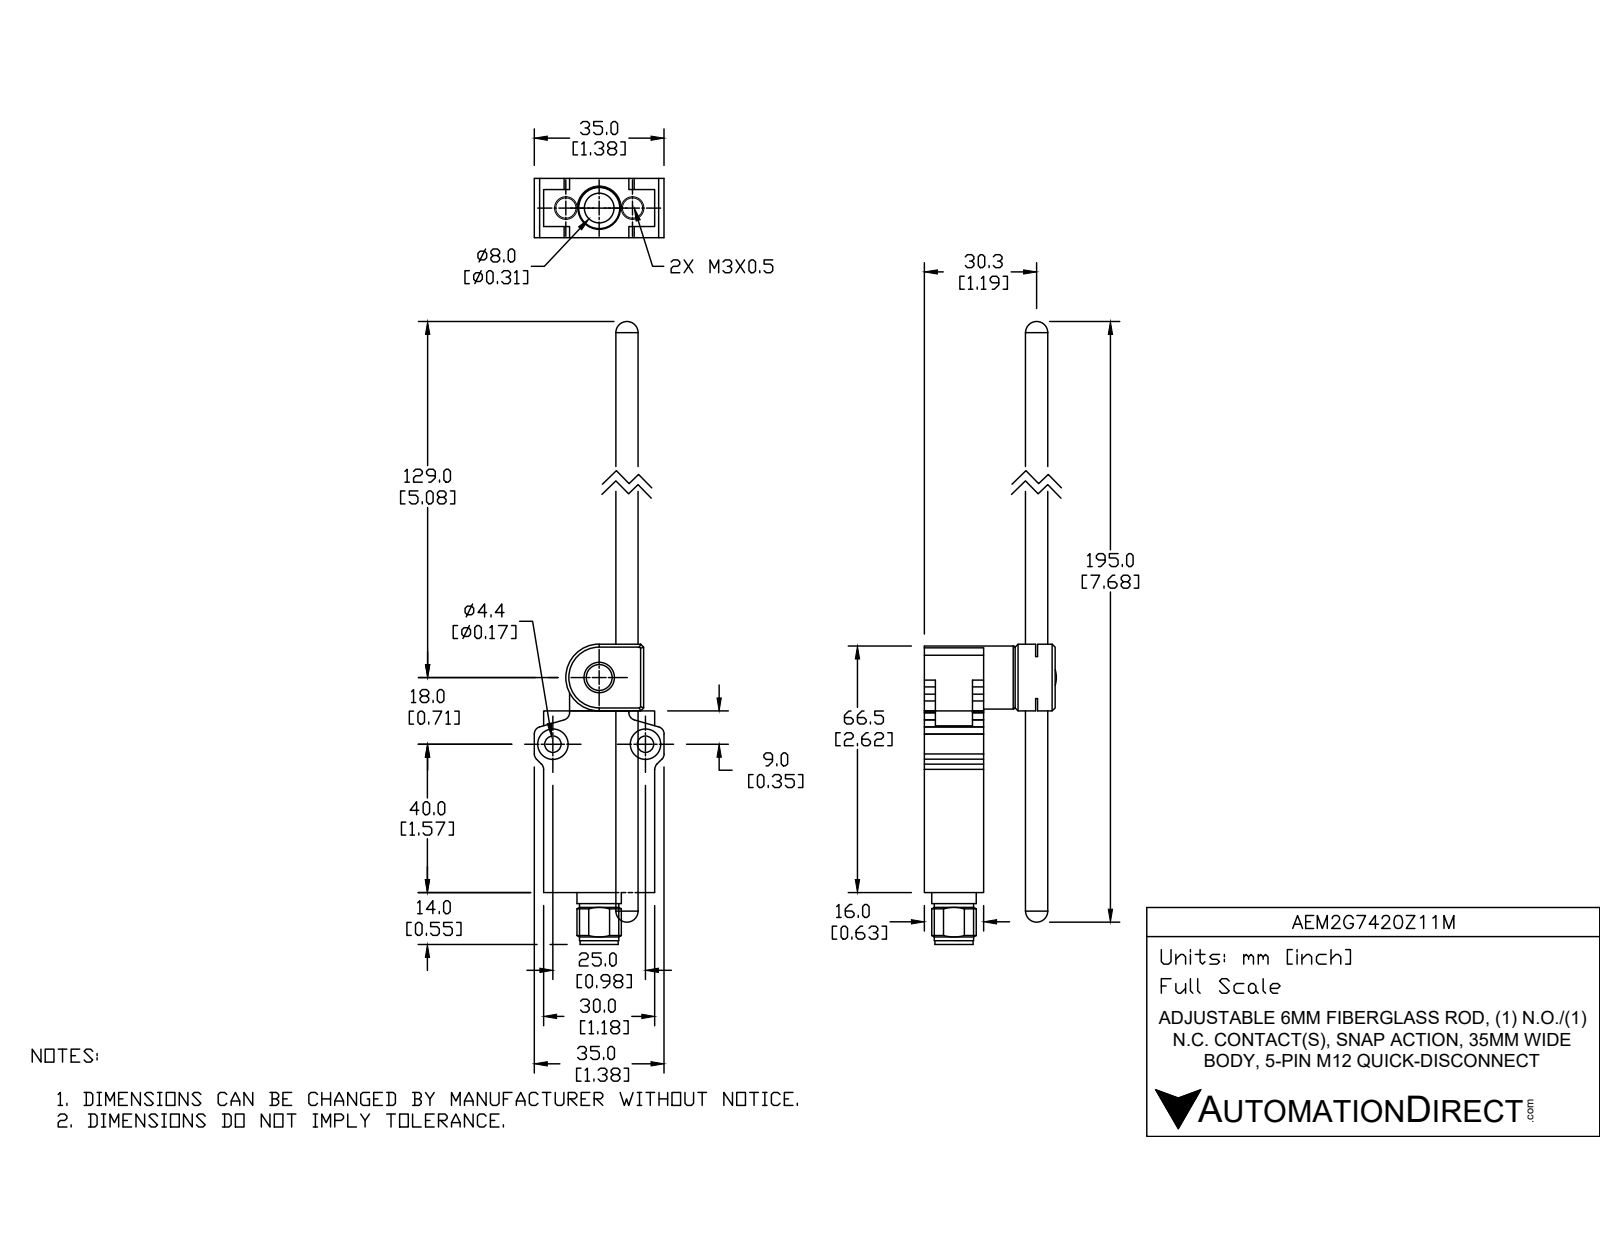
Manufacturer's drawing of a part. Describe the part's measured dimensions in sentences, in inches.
The part is named "AEM2G7420Z11M". Its 3-D file was written by "SolidWorks 2017 (AUTOMOTIVE_DESIGN)". It is 6 solids with 220 faces: 98 planar, 77 cylindrical and 45 other. Overall it measures 8.045 by 1.378 by 1.374 inches. Its volume is 2.344 cubic inches and its surface area 24.09 square inches. Round holes: 2 of diameter 0.118, 2 of diameter 0.173, 2 of diameter 0.323, 1 of diameter 0.138, 1 of diameter 0.197, 1 of diameter 0.236, 1 of diameter 0.315. Round bosses or shafts: 1 of diameter 0.622, 1 of diameter 0.472, 1 of diameter 0.417, 1 of diameter 0.406, 1 of diameter 0.276. Partial cylindrical surfaces (rounded edges, fillets, slot ends): 8 of radius 0.079, 1 of radius 0.256, 1 of radius 0.354. The main face-to-face distances are 0.63, 1.181, 0.177, 0.354, 0.535, 1.165, 0.358, 0.28, 0.902, 2.047. The hole center spacings are 0.866, 0.748, 0.857, 0.984, 1.065.
